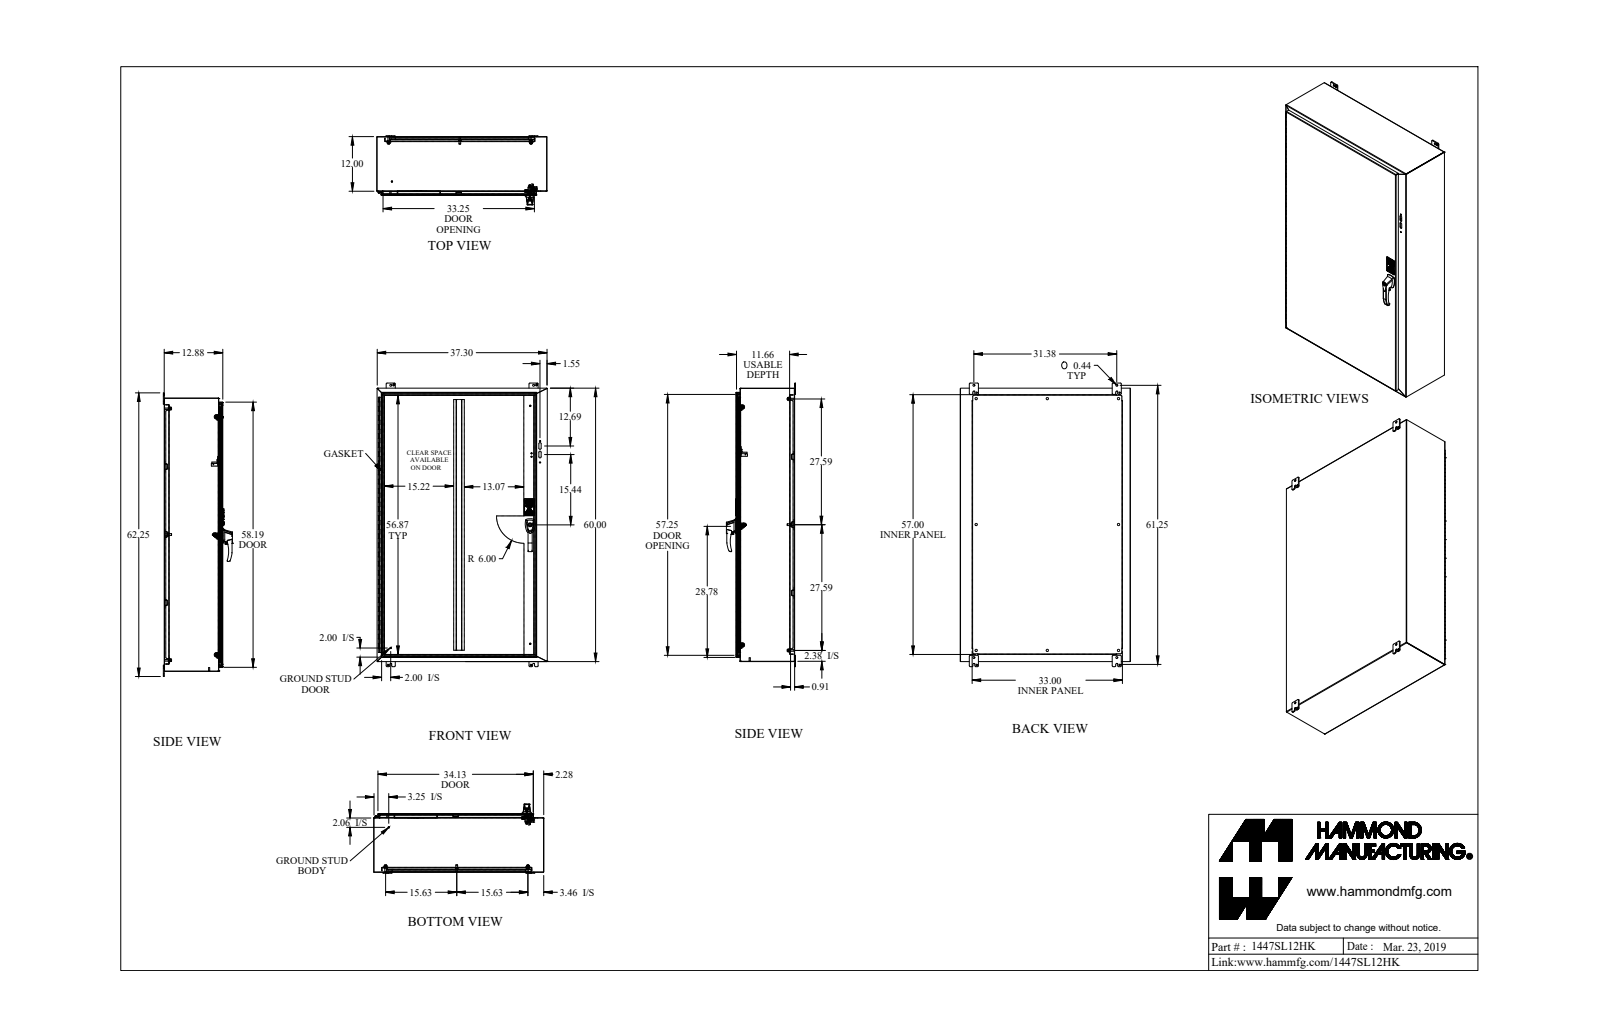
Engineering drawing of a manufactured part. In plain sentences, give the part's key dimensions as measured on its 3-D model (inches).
The part is named "1447SL12HK_Default". Its 3-D file was written by "SolidWorks 2019 (CONFIG_CONTROL_DESIGN)". It is 71 solids with 2172 faces: 1084 planar, 886 cylindrical and 202 other. Overall it measures 62.25 by 37.375 by 15.177 inches. Its volume is 787.1 cubic inches and its surface area 20 231 square inches. Round holes: 8 of diameter 0.5, 6 of diameter 0.176, 6 of diameter 0.313, 4 of diameter 0.307, 4 of diameter 0.437, 4 of diameter 0.445, 3 of diameter 0.25, 3 of diameter 0.265, 3 of diameter 0.413, 2 of diameter 0.156, 2 of diameter 0.173, 2 of diameter 0.196. Round bosses or shafts: 13 of diameter 0.375, 9 of diameter 0.25, 8 of diameter 0.65, 8 of diameter 0.33, 7 of diameter 1, 6 of diameter 0.156, 2 of diameter 0.63, 2 of diameter 0.51. Partial cylindrical surfaces (rounded edges, fillets, slot ends): 33 of radius 0.188, 33 of radius 0.25, 18 of radius 0.036, 18 of radius 0.108, 16 of radius 0.116, 16 of radius 0.125, 10 of radius 0.03, 8 of radius 0.218. The main face-to-face distances are 0.072, 12.803, 12.731, 12.875, 0.095, 11.771, 11.699, 1.032, 1.104, 11.866. The hole center spacings are 31.375, 57.417, 1.11, 31.25, 31.738, 55.25, 1.735, 1.736.
